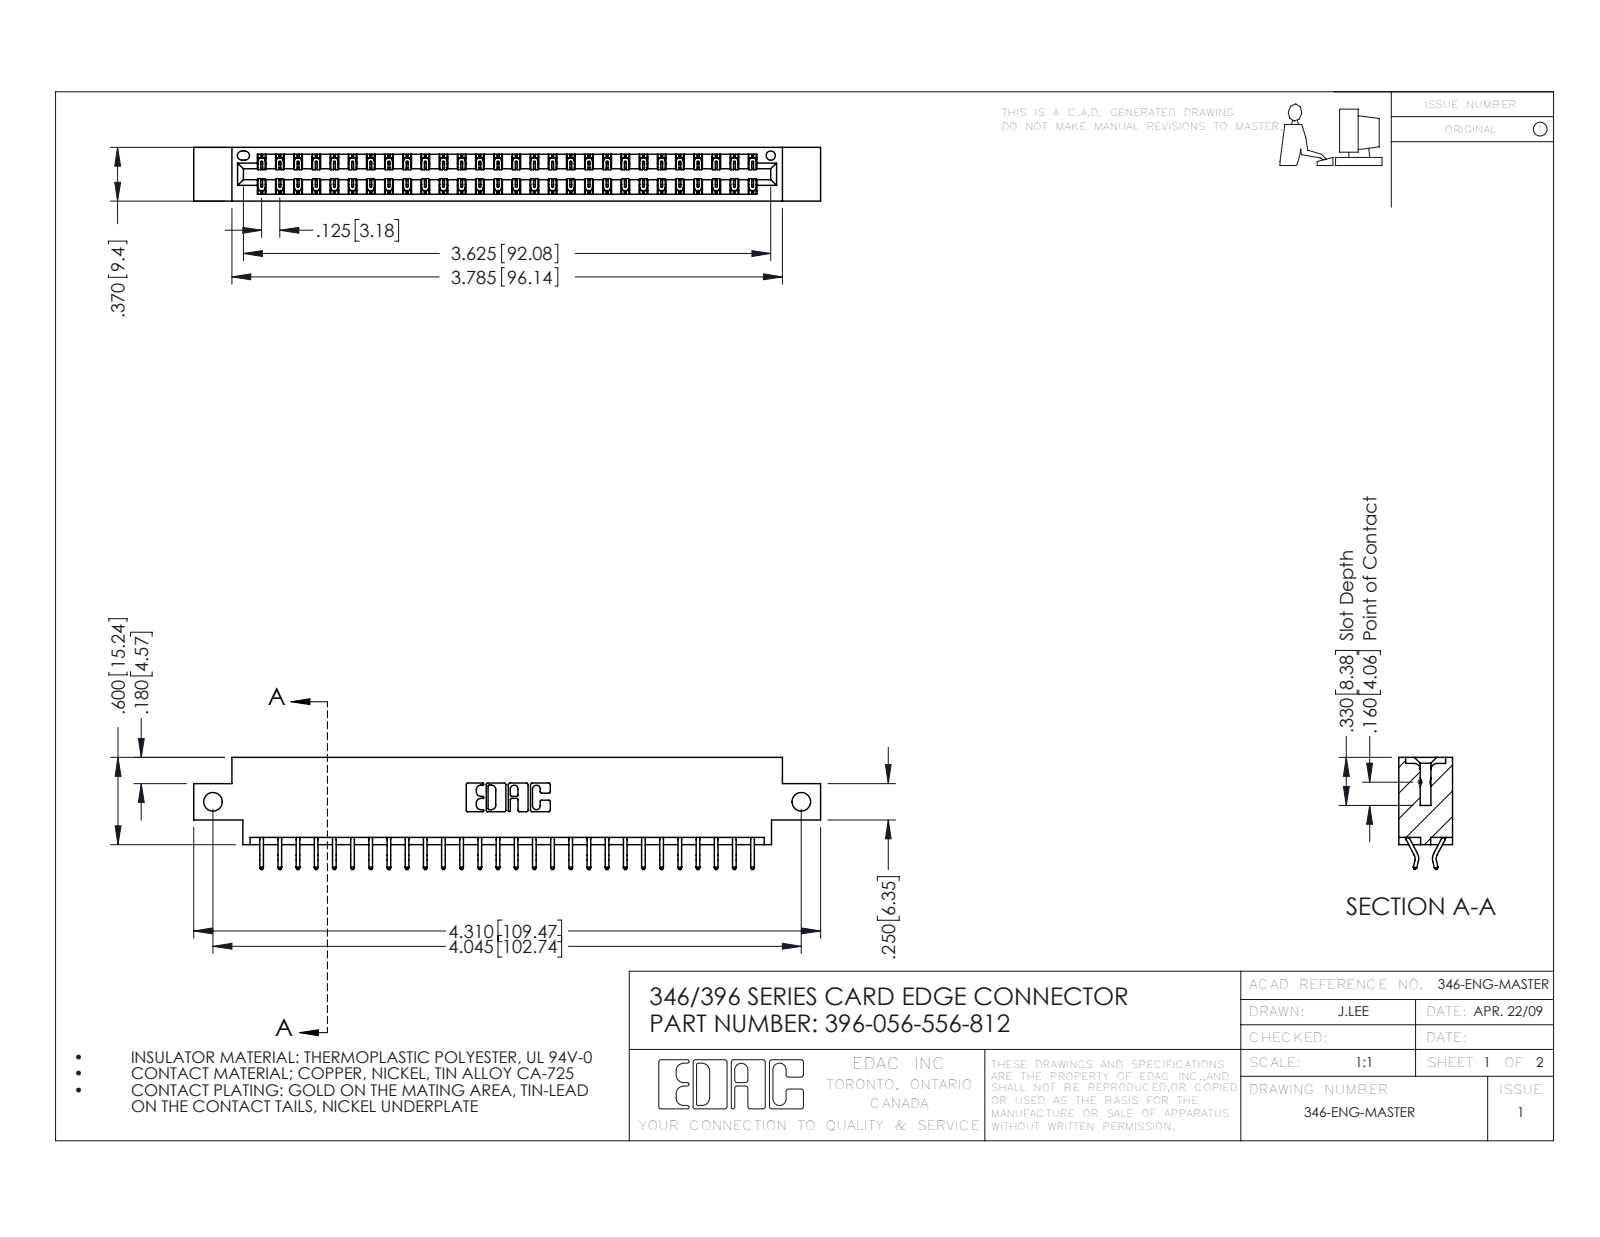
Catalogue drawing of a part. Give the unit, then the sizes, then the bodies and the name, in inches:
Units: inches
Overall size (bounding box): 4.31 × 0.77 × 0.37
Round holes (diameter × count): ⌀0.128 ×2, ⌀0.064 ×1
Partial cylindrical surfaces — rounded edges, fillets, slot ends (radius × count): R0.006 ×84, R0.01 ×22, R0.007 ×6, R0.031 ×6, R0.026 ×3, R0.01 ×2, R0.014 ×2, R0.022 ×2
Main face-to-face distances: 0.048, 0.322, 0.37, 0.25, 0.025, 0.072, 0.298, 0.275, 0.148, 0.222
Hole centre spacings: 4.045
Volume: 0.63 in³ · Surface area: 21.64 in²
Bodies: 57 solids, 3374 faces (2264 planar, 1110 cylindrical, 0 other)
Part name (STEP PRODUCT): 396-056-556-812; 345-292-001_556 Tail; 346 Part_0.170 Offset - Side Mount
STEP written by: SolidWorks 2016 (CONFIG_CONTROL_DESIGN)
